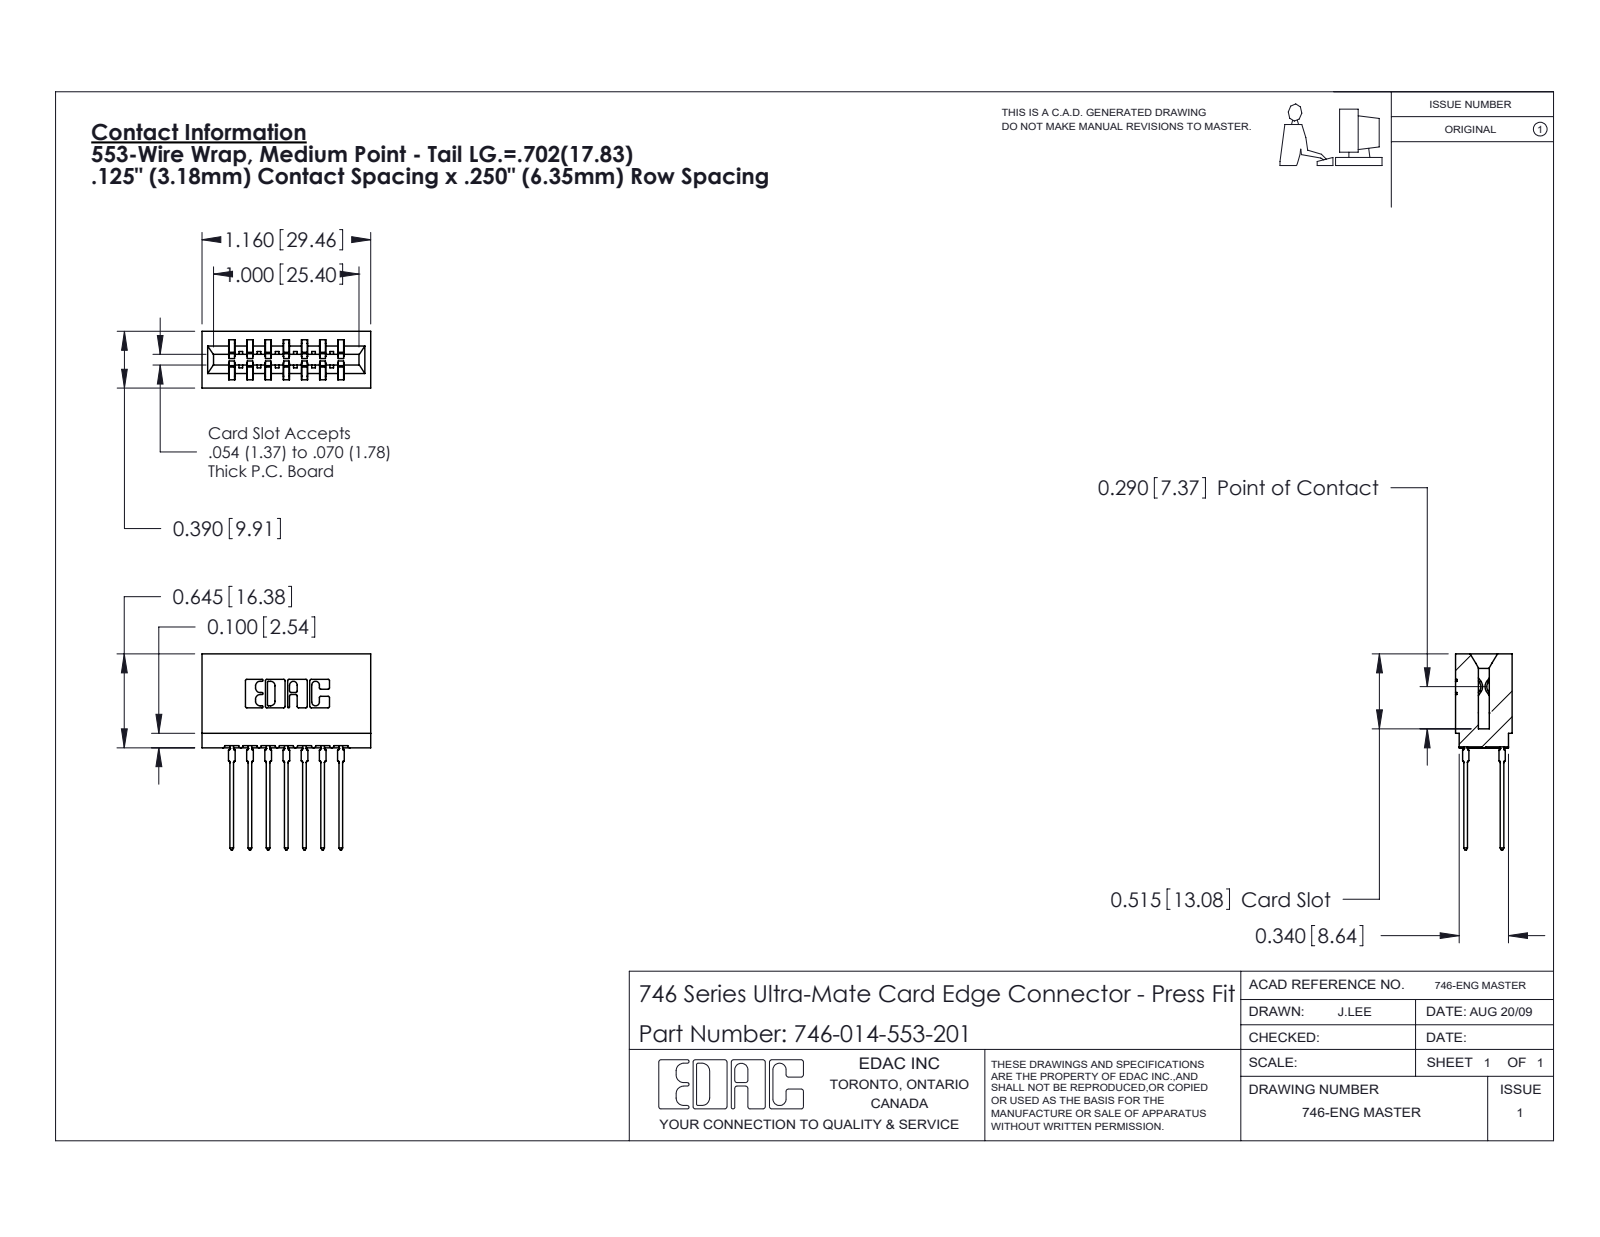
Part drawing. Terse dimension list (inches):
name: 746-292-001_553; 746-014-553-201; 746 Part_.515 Slot Depth - 01
written by: SolidWorks 2020 (CONFIG_CONTROL_DESIGN)
unit: in
bodies: 15 solids, 1350 faces (699 planar, 287 cylindrical, 364 other)
size: 1.346 × 1.16 × 0.39
volume: 0.21 in³; area: 7.93 in²
rounds: 28× R0.021, 22× R0.01, 8× R0.005, 8× R0.011, 8× R0.015, 6× R0.007, 6× R0.031, 3× R0.026
face distances: 0.25, 0.333, 0.057, 0.042, 0.125, 0.125, 0.083, 0.5, 0.025, 0.292
